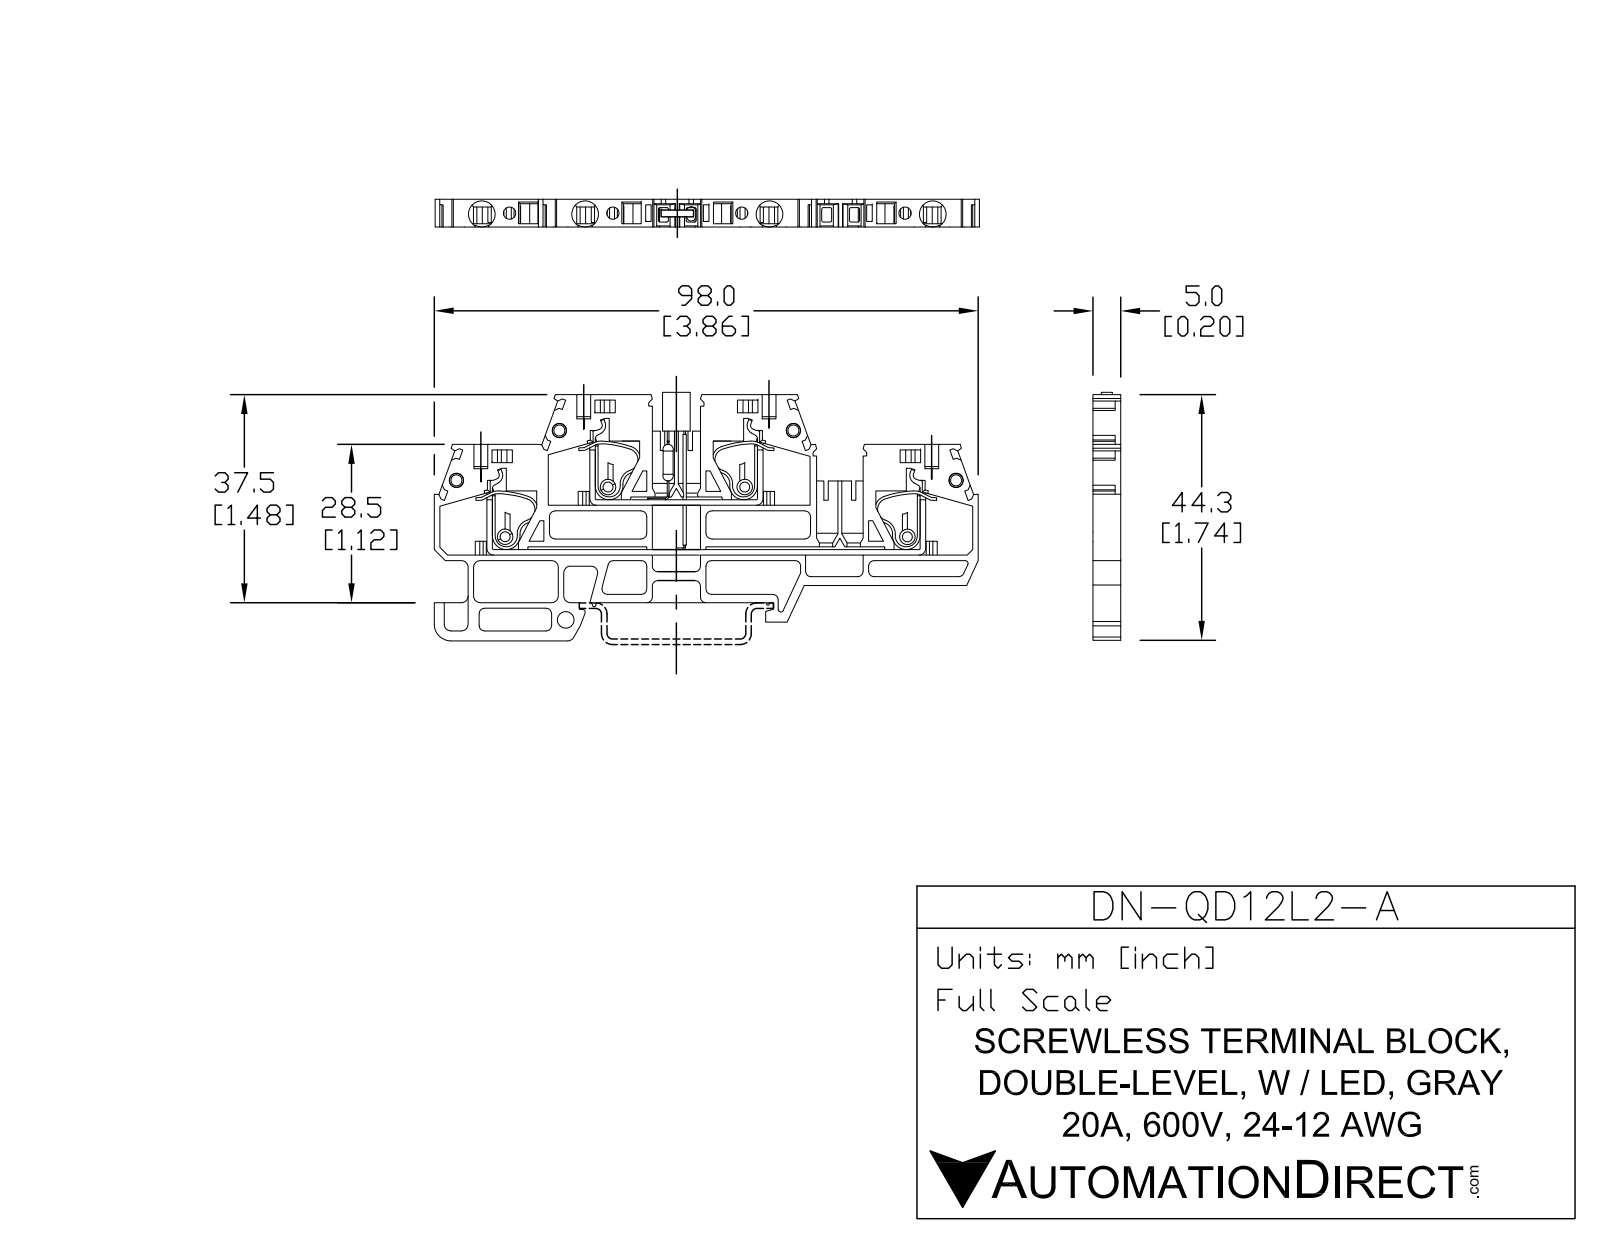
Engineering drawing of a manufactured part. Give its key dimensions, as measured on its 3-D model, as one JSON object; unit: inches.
{"part_name": "DN-QD12L2-A", "step_written_by": "SolidWorks 2017 (AUTOMOTIVE_DESIGN)", "units": "inches", "bodies": {"solids": 1, "faces": 713, "planar": 536, "cylindrical": 129, "other": 48}, "overall_size": [3.858, 1.748, 0.197], "volume_in3": 0.399, "surface_area_in2": 19.43, "round_holes": [[0.087, 4], [0.102, 4], [0.189, 4], [0.118, 1]], "round_bosses_or_shafts": [[0.11, 4]], "partial_cylinders_radius": [[0.039, 23], [0.047, 12], [0.043, 8], [0.02, 4], [0.028, 4], [0.055, 4], [0.012, 1], [0.118, 1]], "face_to_face_distances": [0.197, 0.039, 0.031, 0.165, 0.079, 0.118, 0.114, 0.028, 0.394, 0.059], "hole_center_spacings": [0.197, 0.732, 1.11, 1.157, 1.843, 2.268, 3, 0.535]}
